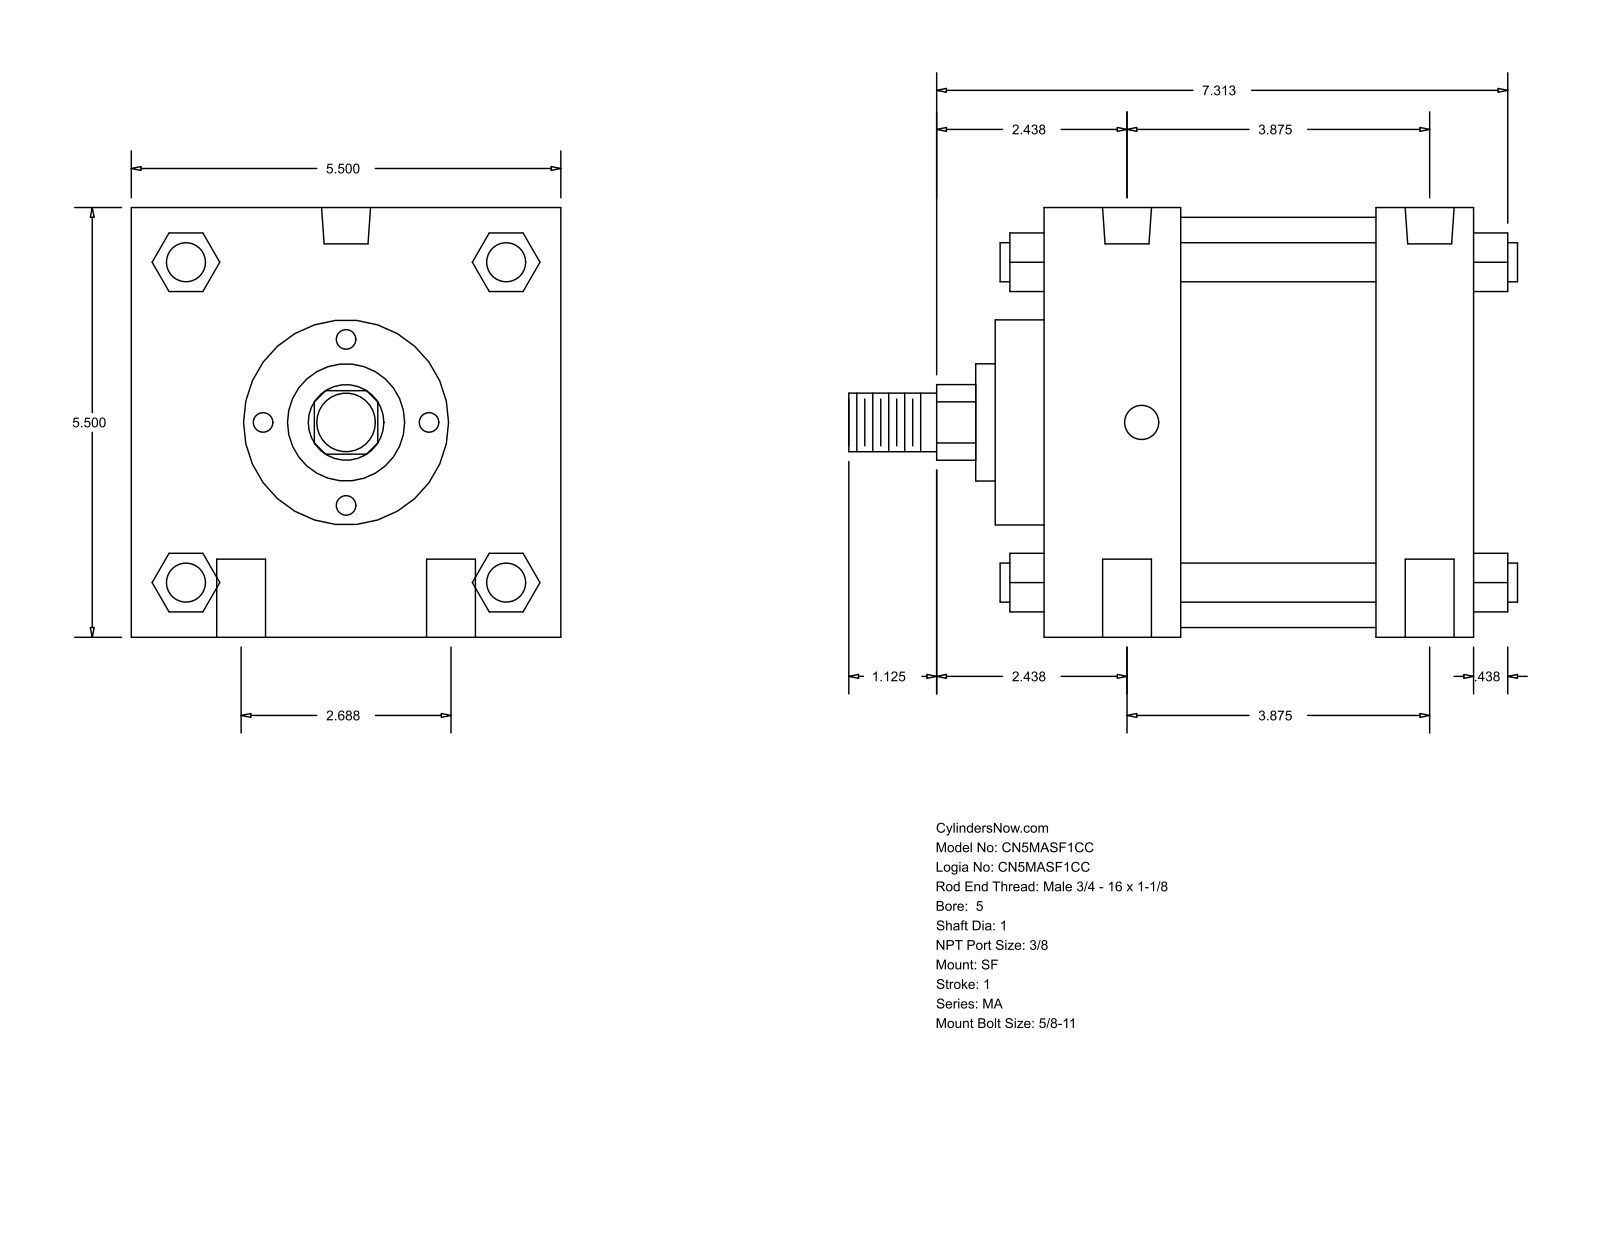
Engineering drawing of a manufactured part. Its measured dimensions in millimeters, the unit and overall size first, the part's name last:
Units: millimetres
Overall size (bounding box): 217.49 × 139.7 × 139.7
Round holes (diameter × count): ⌀15.88 ×4, ⌀11.11 ×2, ⌀15.93 ×2
Round bosses / shafts (diameter × count): ⌀12.7 ×4, ⌀133.35 ×1, ⌀66.67 ×1, ⌀38.1 ×1, ⌀25.4 ×1, ⌀19.05 ×1
Partial cylindrical surfaces — rounded edges, fillets, slot ends (radius × count): R12.29 ×1
Main face-to-face distances: 139.7, 44.46, 107.96, 63.5, 95.24, 31.74, 15.87, 60.33, 123.83, 155.57
Hole centre spacings: 34.13, 104.18, 98.43, 68.26, 119.78, 88.9
Bodies: 0 solids, 126 faces (95 planar, 31 cylindrical, 0 other)
Part name (STEP PRODUCT): MA_SF__0500_1
STEP written by: GSSL Pune (CONFIG_CONTROL_DESIGN)
